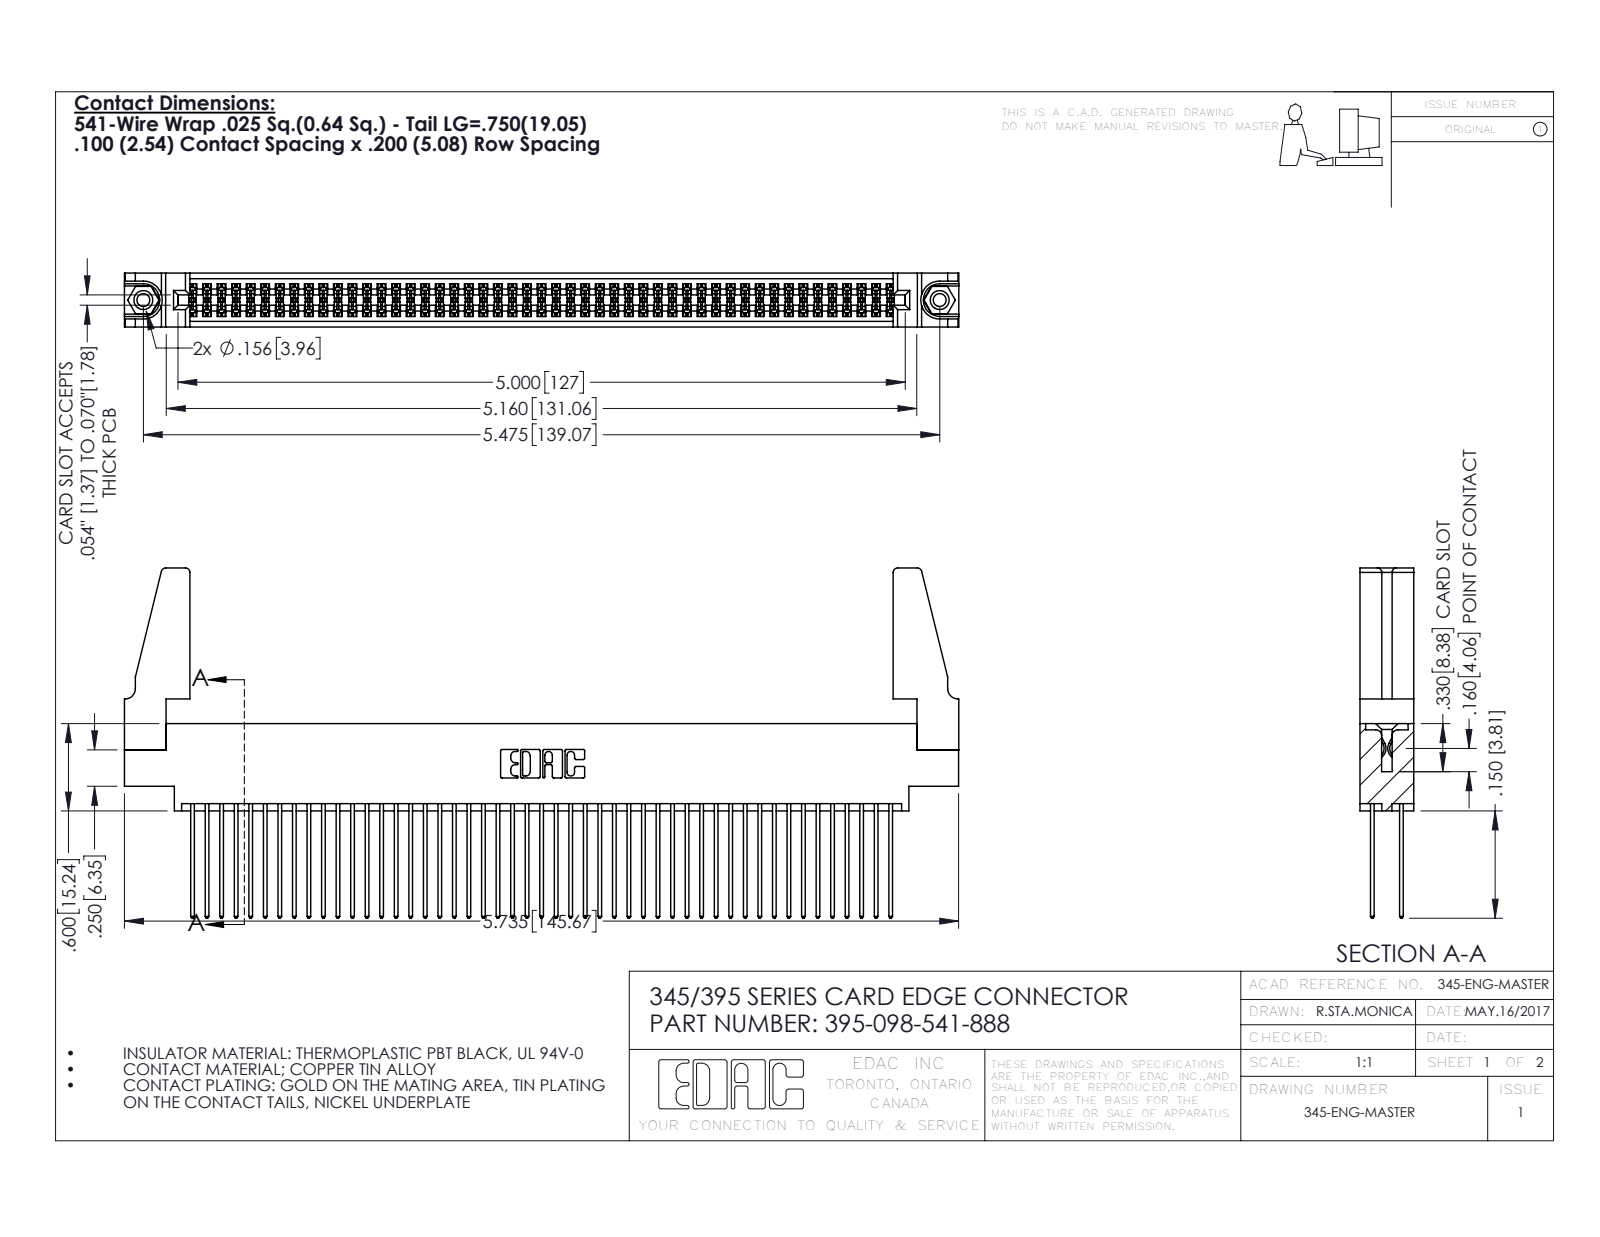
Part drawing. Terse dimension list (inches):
name: 345 Part_0.170 Offset - 0.156 Dia-TH; 345-292-001_345-293-141; 345-250-001_345-250-001-102; 395-098-541-888 (+1 more)
written by: SolidWorks 2016 (CONFIG_CONTROL_DESIGN)
unit: in
bodies: 103 solids, 5154 faces (3390 planar, 1748 cylindrical, 16 other)
size: 5.736 × 2.407 × 0.37
volume: 1.093 in³; area: 42.97 in²
holes: 2× ⌀0.089, 2× ⌀0.125, 2× ⌀0.156, 1× ⌀0.064
bosses: 2× ⌀0.155
rounds: 147× R0.006, 98× R0.01, 22× R0.01, 8× R0.03, 6× R0.007, 6× R0.031, 3× R0.026, 2× R0.014
face distances: 0.072, 0.298, 0.098, 0.272, 0.025, 0.2, 0.37, 0.225, 0.175, 0.149
hole spacings: 0.27, 5.239, 5.475
